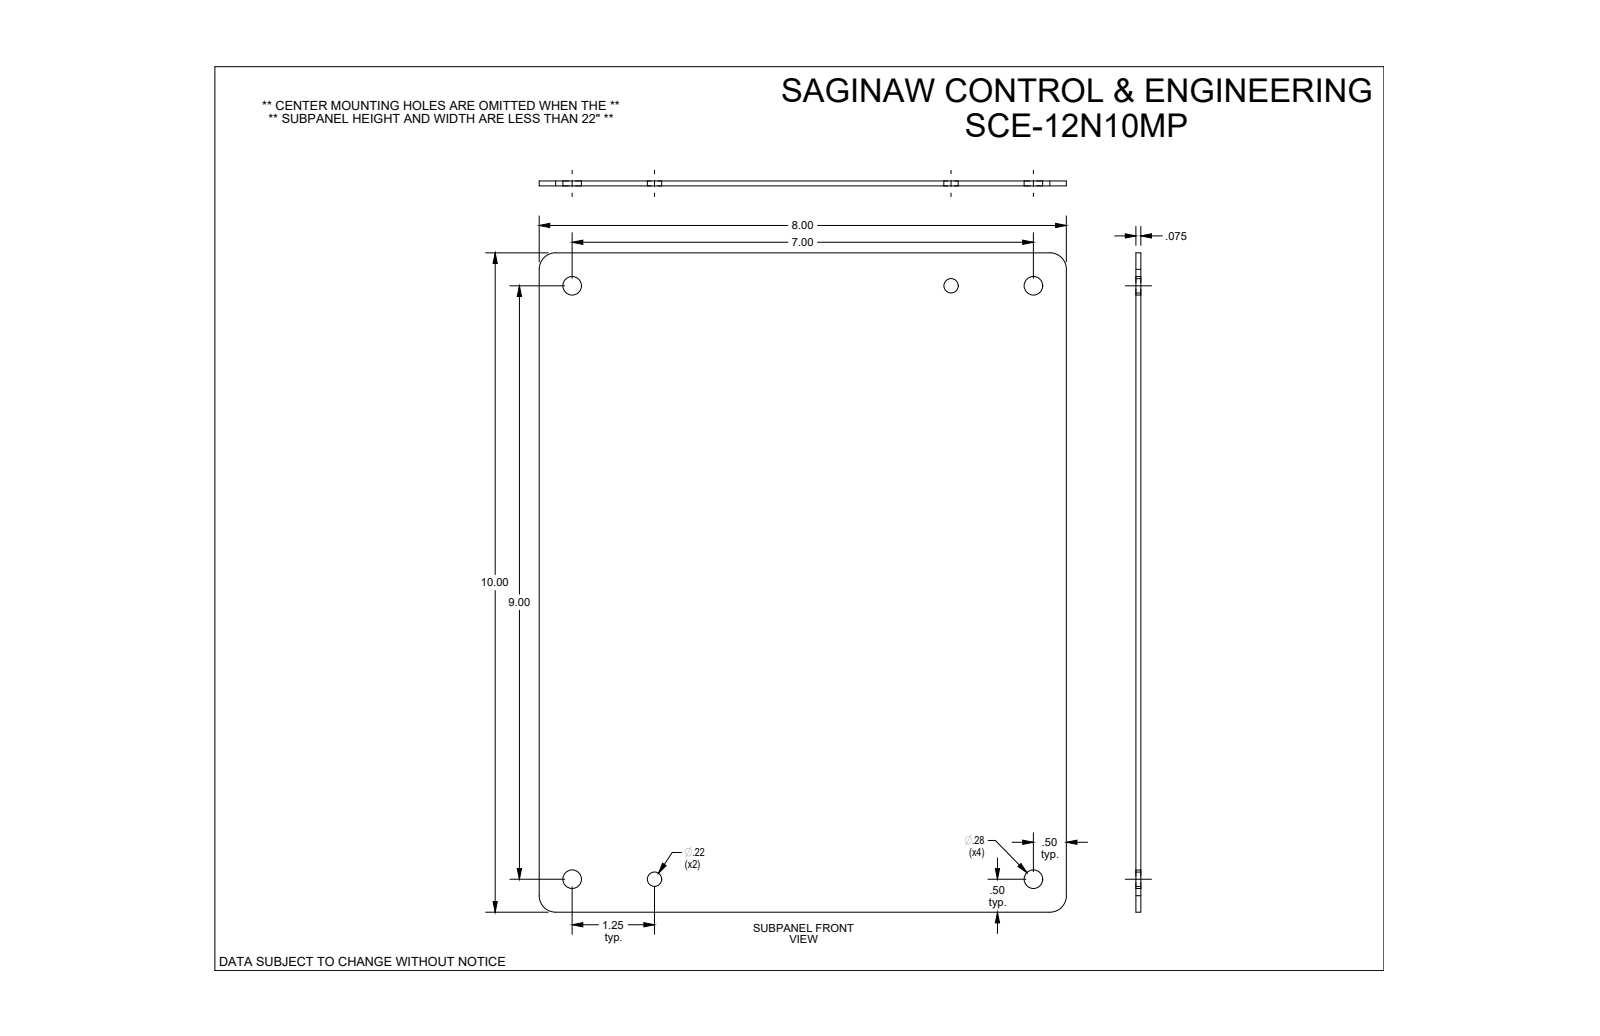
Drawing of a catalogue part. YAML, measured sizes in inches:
part_name: "SCE-12N10MP"
step_written_by: "SolidWorks 2019 (CONFIG_CONTROL_DESIGN)"
units: inches
bodies: {solids: 1, faces: 16, planar: 6, cylindrical: 10, other: 0}
overall_size: [10, 8, 0.075]
volume: 5.972
surface_area: 162.3
round_holes:
  - {diameter: 0.281, count: 4}
  - {diameter: 0.218, count: 2}
partial_cylinders:
  - {radius: 0.25, count: 4}
face_to_face_distances: [0.075, 8, 10]
hole_center_spacings: [1.25, 5.75, 7, 9, 9.086, 10.68, 11.402, 10.062]
